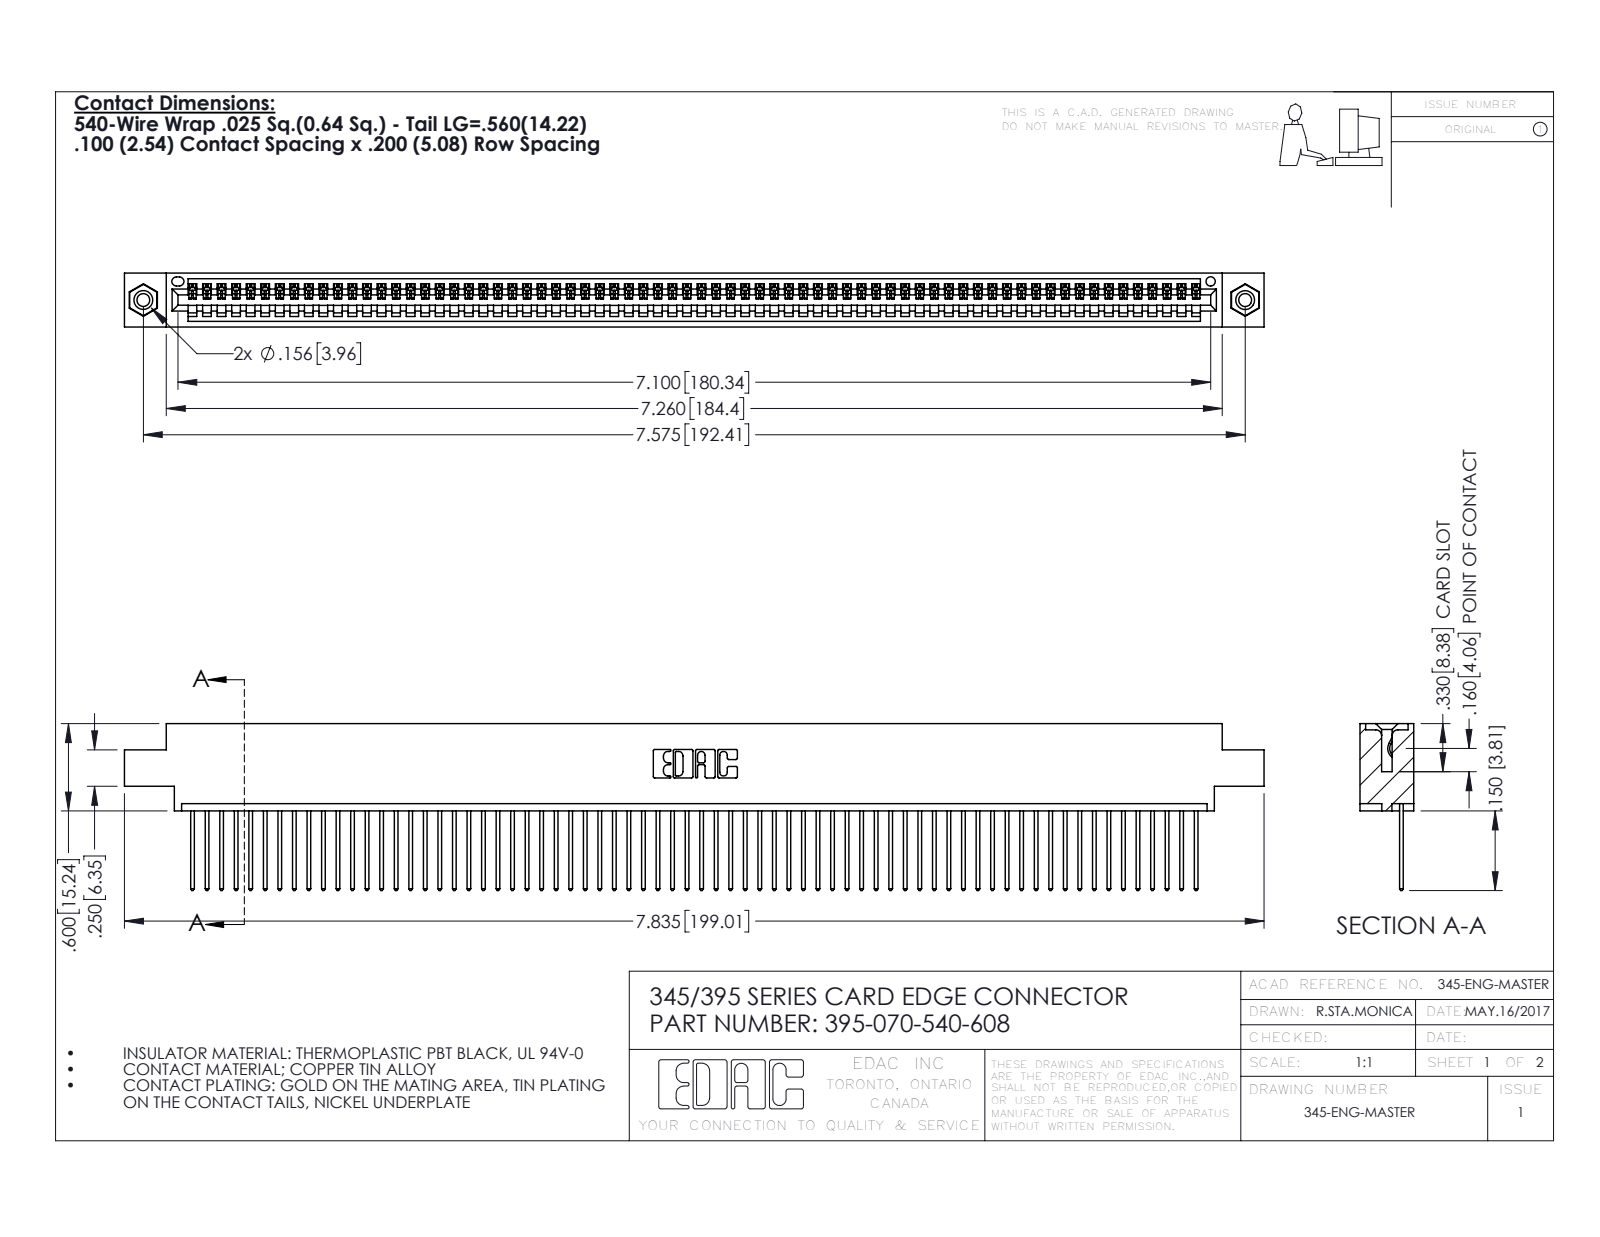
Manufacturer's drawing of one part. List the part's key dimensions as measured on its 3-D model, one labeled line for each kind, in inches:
Part name (STEP PRODUCT): 345-292-001_345-293-140; 345-250-001_345-250-003-102; 395-070-540-608; 345 Part_0.170 Offset - 0.156 Dia-TI
STEP written by: SolidWorks 2016 (CONFIG_CONTROL_DESIGN)
Units: inches
Bodies: 73 solids, 4250 faces (2916 planar, 1318 cylindrical, 16 other)
Overall size (bounding box): 7.835 × 1.147 × 0.37
Volume: 1.166 in³ · Surface area: 41.23 in²
Round holes (diameter × count): ⌀0.089 ×2, ⌀0.125 ×2, ⌀0.156 ×2, ⌀0.064 ×1
Round bosses / shafts (diameter × count): ⌀0.155 ×2
Partial cylindrical surfaces — rounded edges, fillets, slot ends (radius × count): R0.006 ×140, R0.01 ×140, R0.01 ×22, R0.007 ×6, R0.031 ×6, R0.026 ×3, R0.031 ×2, R0.04 ×2
Main face-to-face distances: 0.072, 0.298, 0.37, 0.098, 0.272, 0.025, 0.2, 0.225, 0.175, 0.149
Hole centre spacings: 0.27, 7.339, 7.575
